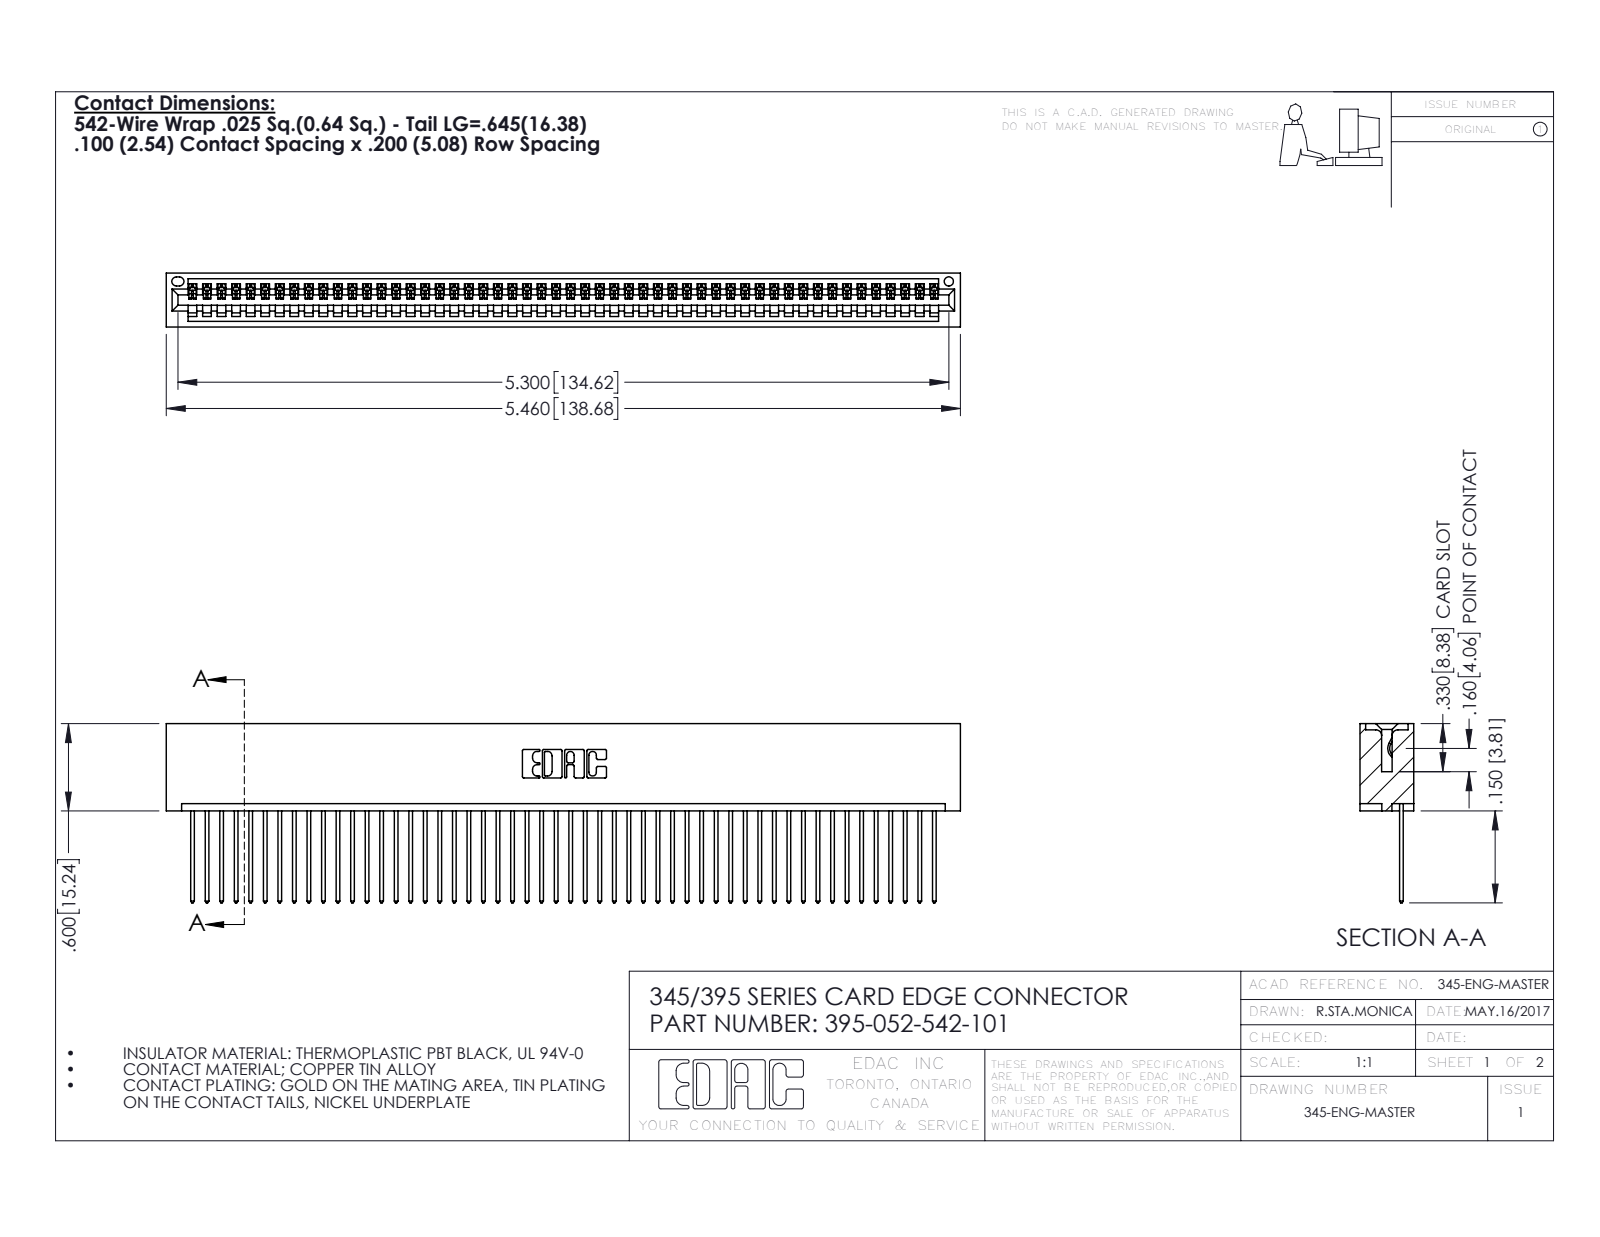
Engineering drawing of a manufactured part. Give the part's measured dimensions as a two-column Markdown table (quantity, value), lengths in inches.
| quantity | value |
| --- | --- |
| part name | 395-052-542-101; 345-292-001_345-293-142; 345 Part_No Mounting Lugs |
| STEP written by | SolidWorks 2016 (CONFIG_CONTROL_DESIGN) |
| units | inches |
| bodies | 53 solids, 3134 faces (2156 planar, 978 cylindrical, 0 other) |
| overall size | 5.46 × 1.232 × 0.37 |
| volume | 0.852 in³ |
| surface area | 30.38 in² |
| round holes (diameter × count) | 0.064 × 1 |
| partial cylindrical surfaces (radius × count) | 0.006 × 104, 0.01 × 104, 0.01 × 22, 0.007 × 6, 0.031 × 6, 0.026 × 3, 0.031 × 2, 0.04 × 2 |
| main face-to-face distances | 0.072, 0.298, 0.098, 0.272, 0.025, 0.37, 0.2, 0.225, 0.149, 0.072 |
